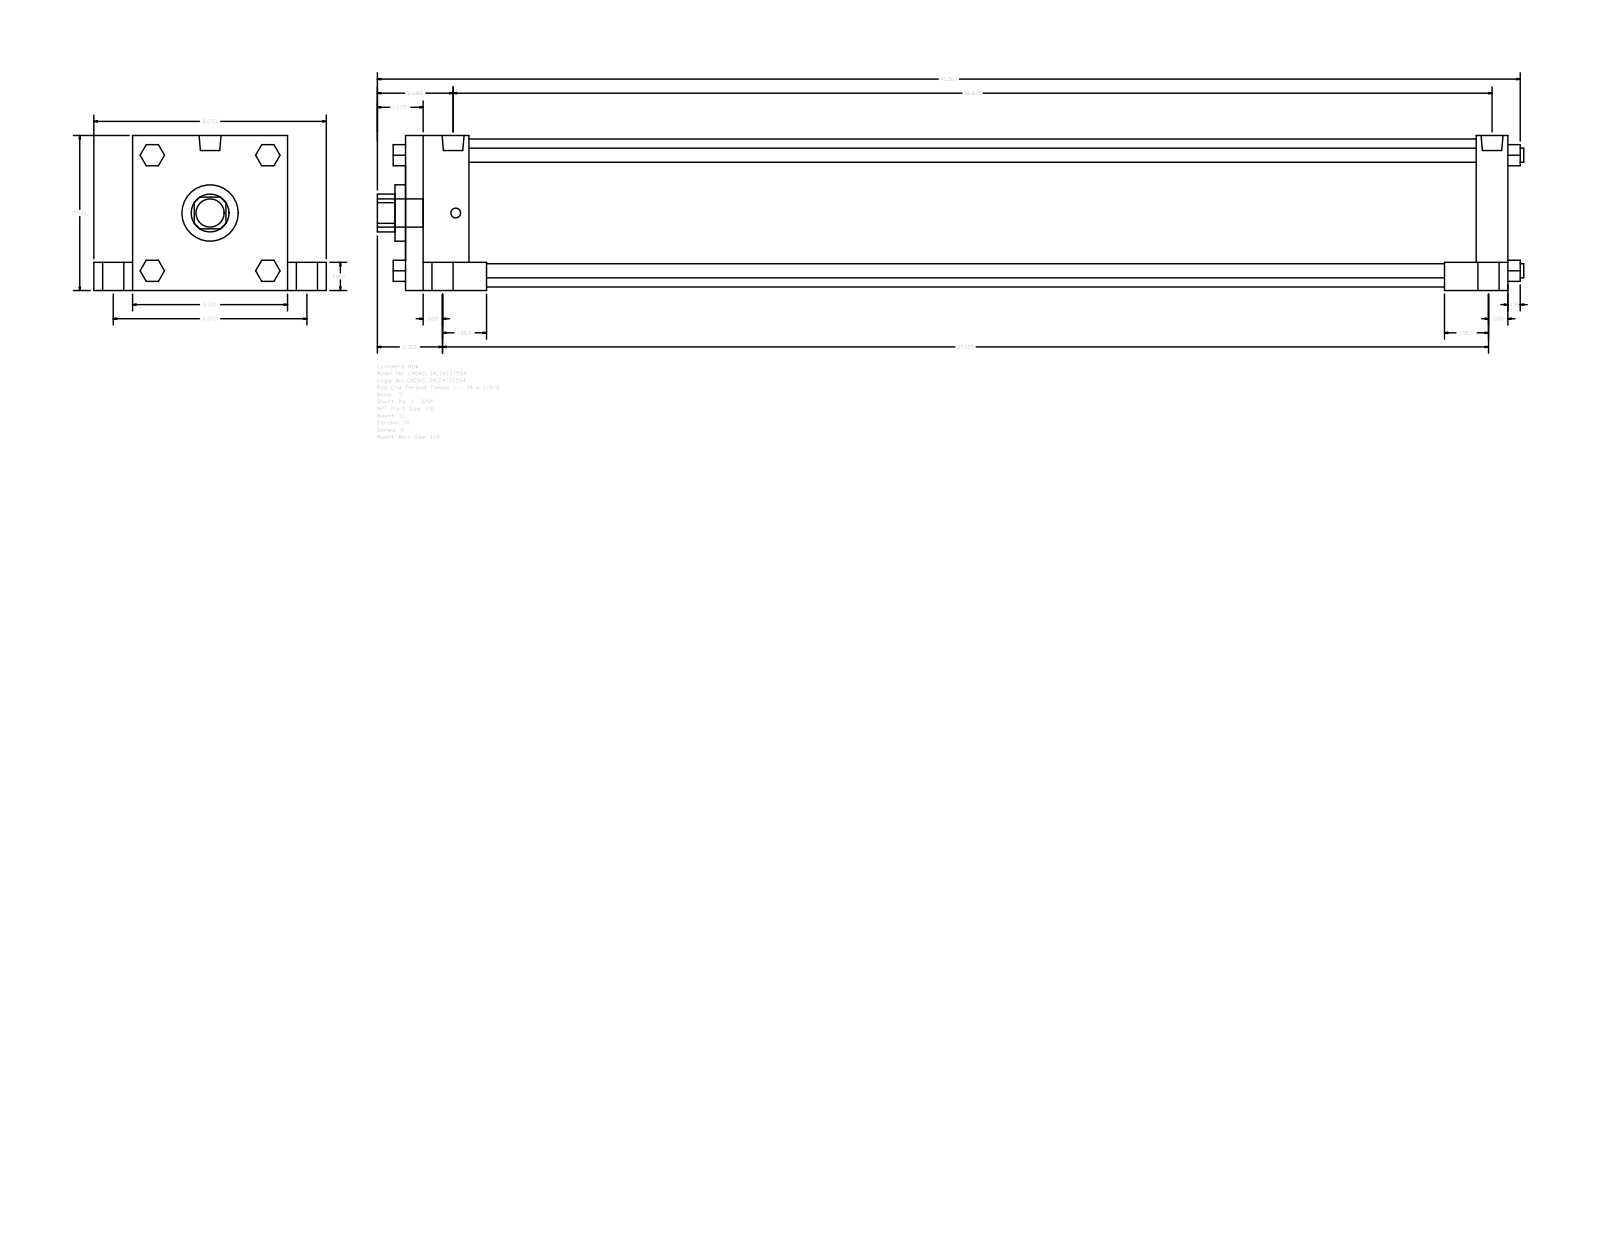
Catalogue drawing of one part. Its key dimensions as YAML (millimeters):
part_name: "A_SL__0500_1.375"
step_written_by: "GSSL Pune (CONFIG_CONTROL_DESIGN)"
units: millimeters
bodies: {solids: 0, faces: 150, planar: 114, cylindrical: 36, other: 0}
overall_size: [1033.46, 209.55, 139.7]
round_holes:
  - {diameter: 34.92, count: 1}
  - {diameter: 50.8, count: 1}
  - {diameter: 133.35, count: 1}
round_bosses_or_shafts:
  - {diameter: 25.4, count: 5}
  - {diameter: 19.05, count: 4}
  - {diameter: 12.7, count: 4}
  - {diameter: 8.73, count: 4}
  - {diameter: 19.77, count: 2}
partial_cylinders:
  - {radius: 17.06, count: 1}
face_to_face_distances: [139.7, 993.77, 57.15, 936.62, 25.4, 114.3, 34.93, 174.63, 28.57, 965.2]
